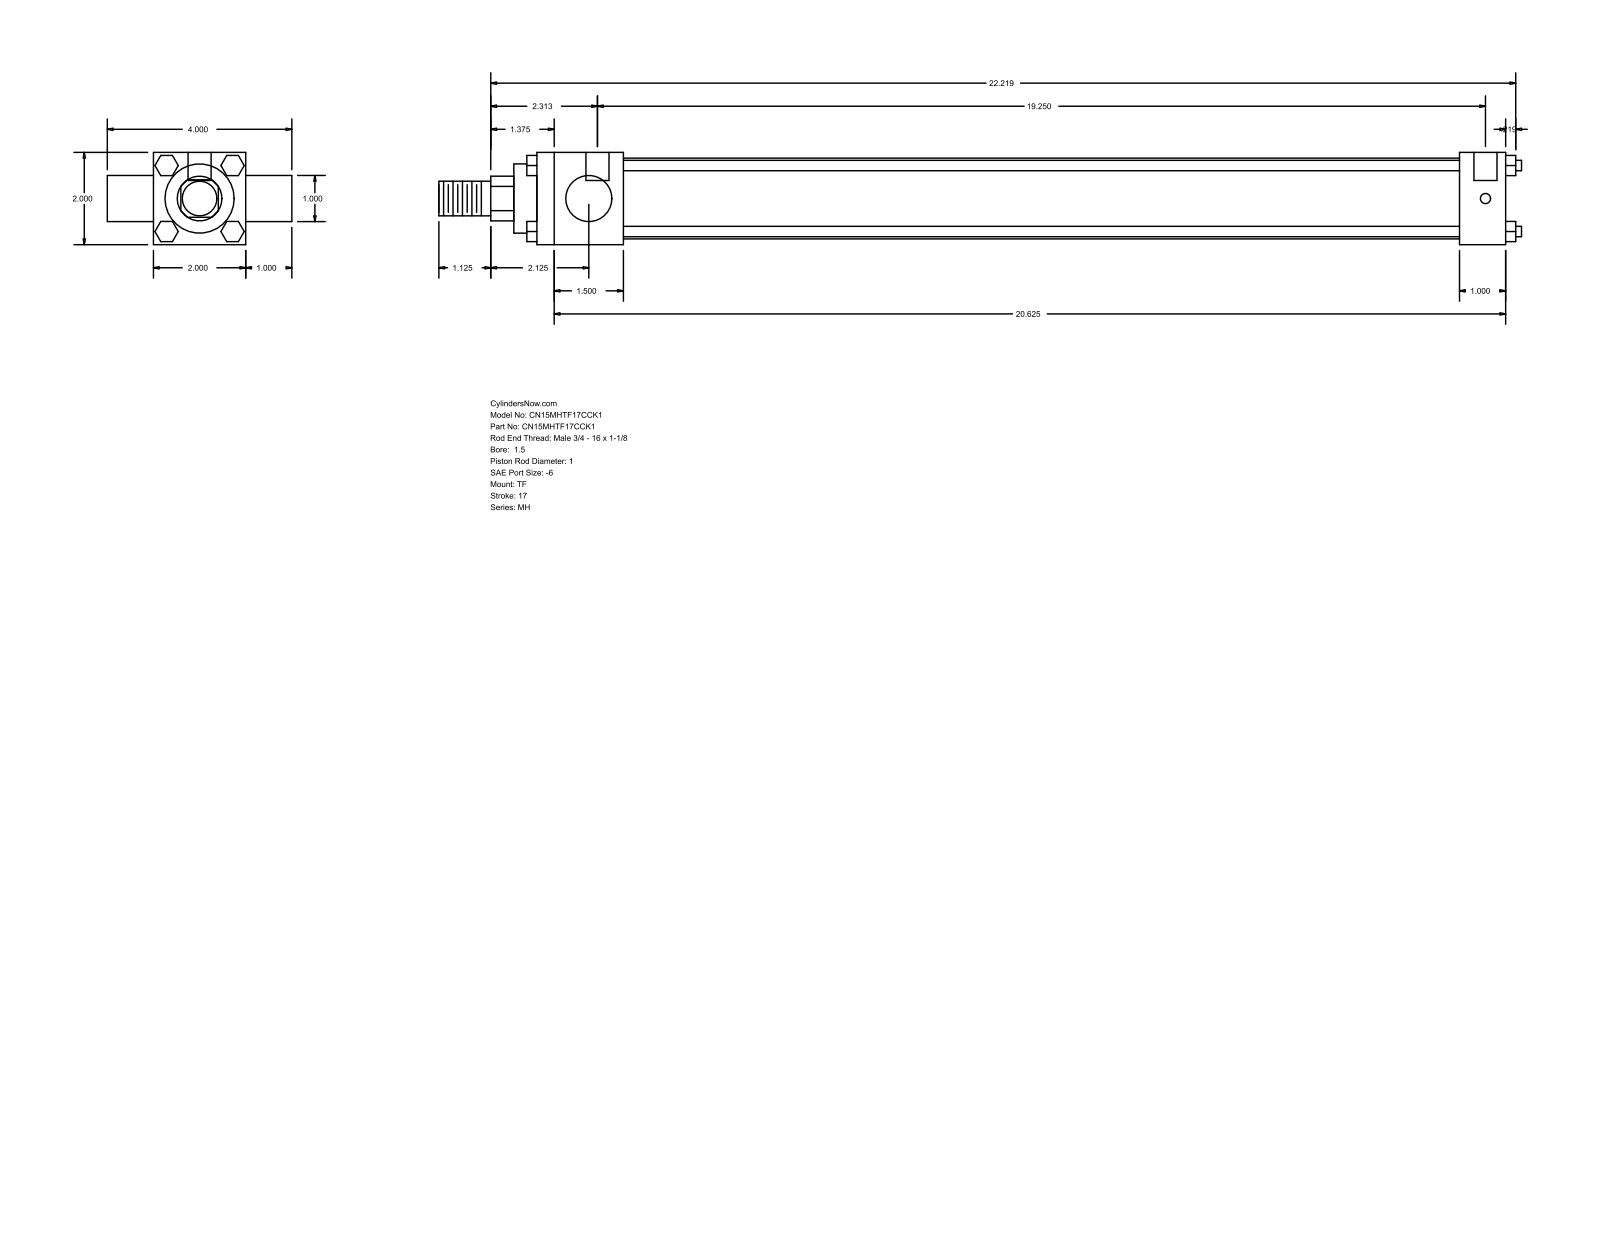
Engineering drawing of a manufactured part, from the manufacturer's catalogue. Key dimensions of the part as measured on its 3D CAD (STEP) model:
Part name (STEP PRODUCT): MH_TF__0150_1
STEP written by: GSSL Pune (CONFIG_CONTROL_DESIGN)
Units: millimetres
Bodies: 0 solids, 120 faces (92 planar, 28 cylindrical, 0 other)
Overall size (bounding box): 596.11 × 101.6 × 50.8
Round holes (diameter × count): ⌀5.56 ×3, ⌀12.7 ×2
Round bosses / shafts (diameter × count): ⌀5.71 ×4, ⌀25.4 ×2, ⌀44.45 ×1, ⌀38.1 ×1, ⌀19.05 ×1
Partial cylindrical surfaces — rounded edges, fillets, slot ends (radius × count): R12.29 ×1
Main face-to-face distances: 50.8, 25.4, 533.4, 76.2, 47.63, 485.77, 508, 460.37, 101.6, 12.7
Hole centre spacings: 3.18, 488.95, 492.13
